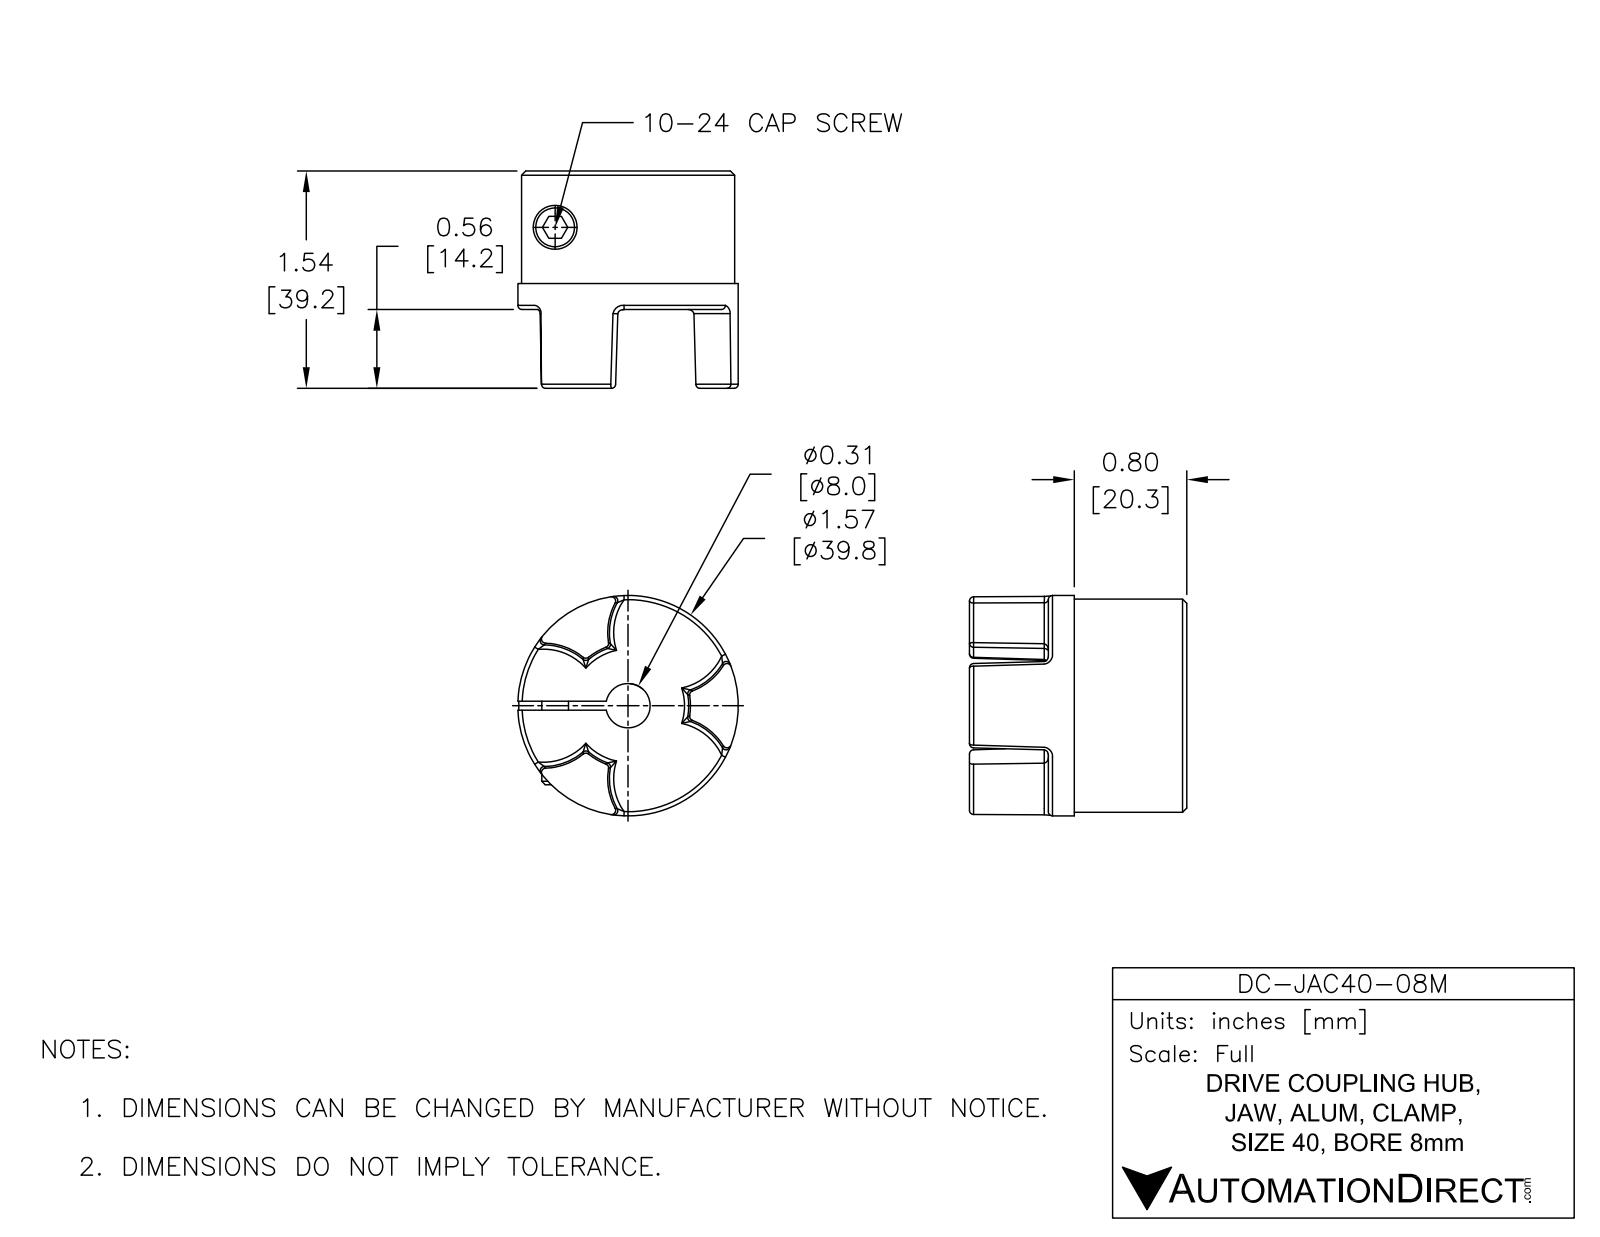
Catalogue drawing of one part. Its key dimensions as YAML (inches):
part_name: "DC-JAC40-08M"
step_written_by: "SolidWorks 2015 (AUTOMOTIVE_DESIGN)"
units: inches
bodies: {solids: 1, faces: 106, planar: 9, cylindrical: 18, other: 79}
overall_size: [1.566, 1.565, 1.544]
volume: 1.861
surface_area: 13.28
round_holes:
  - {diameter: 0.145, count: 1}
  - {diameter: 0.201, count: 1}
  - {diameter: 0.315, count: 1}
  - {diameter: 0.329, count: 1}
round_bosses_or_shafts:
  - {diameter: 1.566, count: 1}
  - {diameter: 1.515, count: 1}
partial_cylinders:
  - {radius: 0.478, count: 1}
face_to_face_distances: [0.984, 0.063, 1.544, 0.56, 0.799, 0.185, 0.745, 0.157, 0.22]
